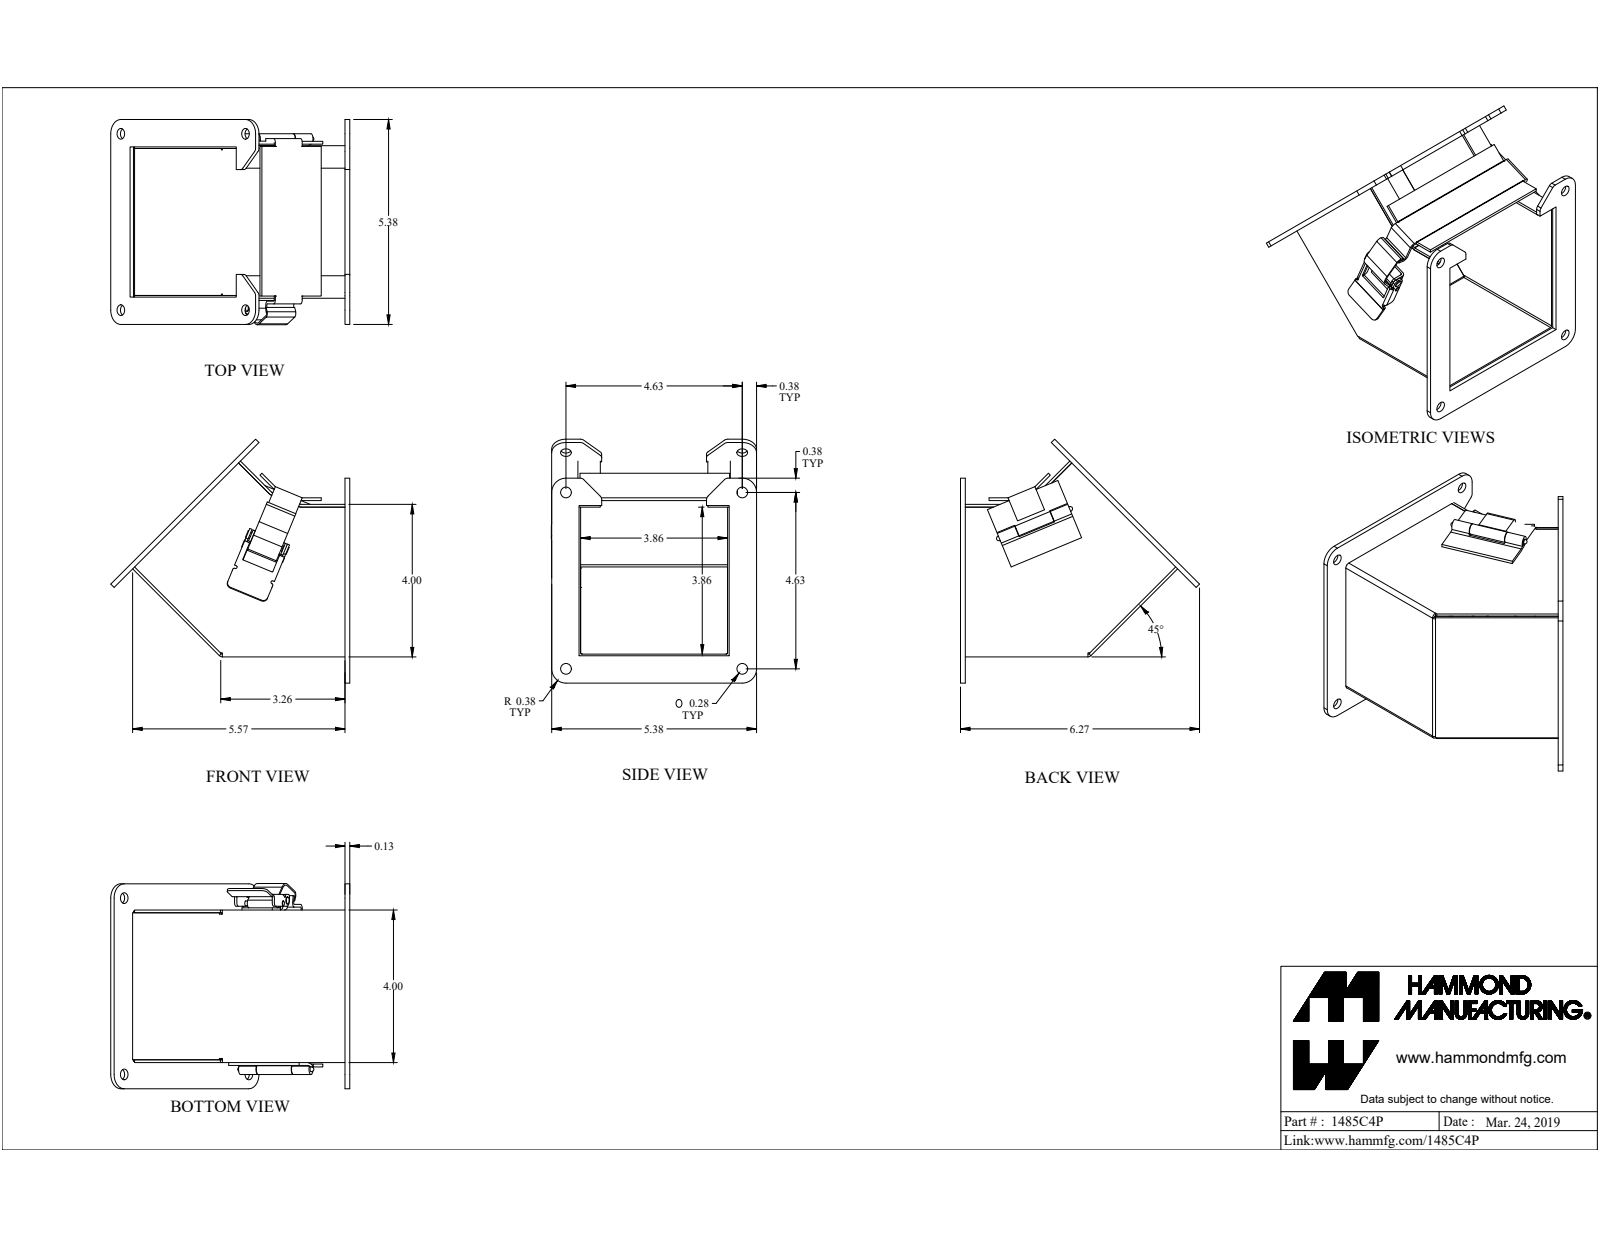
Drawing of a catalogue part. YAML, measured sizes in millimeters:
part_name: "1485C4P"
step_written_by: "SolidWorks 2019 (CONFIG_CONTROL_DESIGN)"
units: millimeters
bodies: {solids: 12, faces: 307, planar: 198, cylindrical: 107, other: 2}
overall_size: [162.5, 159.3, 136.7]
volume: 141900
surface_area: 146700
round_holes:
  - {diameter: 7.1, count: 8}
  - {diameter: 3.2, count: 2}
  - {diameter: 3.3, count: 2}
  - {diameter: 4.2, count: 2}
round_bosses_or_shafts:
  - {diameter: 4.7, count: 3}
  - {diameter: 4, count: 2}
  - {diameter: 7, count: 1}
  - {diameter: 7, count: 1}
  - {diameter: 3.2, count: 1}
partial_cylinders:
  - {radius: 3.2, count: 12}
  - {radius: 0.9, count: 10}
  - {radius: 2.7, count: 10}
  - {radius: 9.5, count: 8}
  - {radius: 0.4, count: 7}
  - {radius: 0.9, count: 4}
  - {radius: 1, count: 4}
  - {radius: 1.9, count: 3}
face_to_face_distances: [1.8, 99.8, 3.2, 101.6, 97.9, 4.4, 104.1, 104.1, 4.4, 1.9]
hole_center_spacings: [117.5, 112.4, 113.3, 166.1, 7.2, 7.2]
